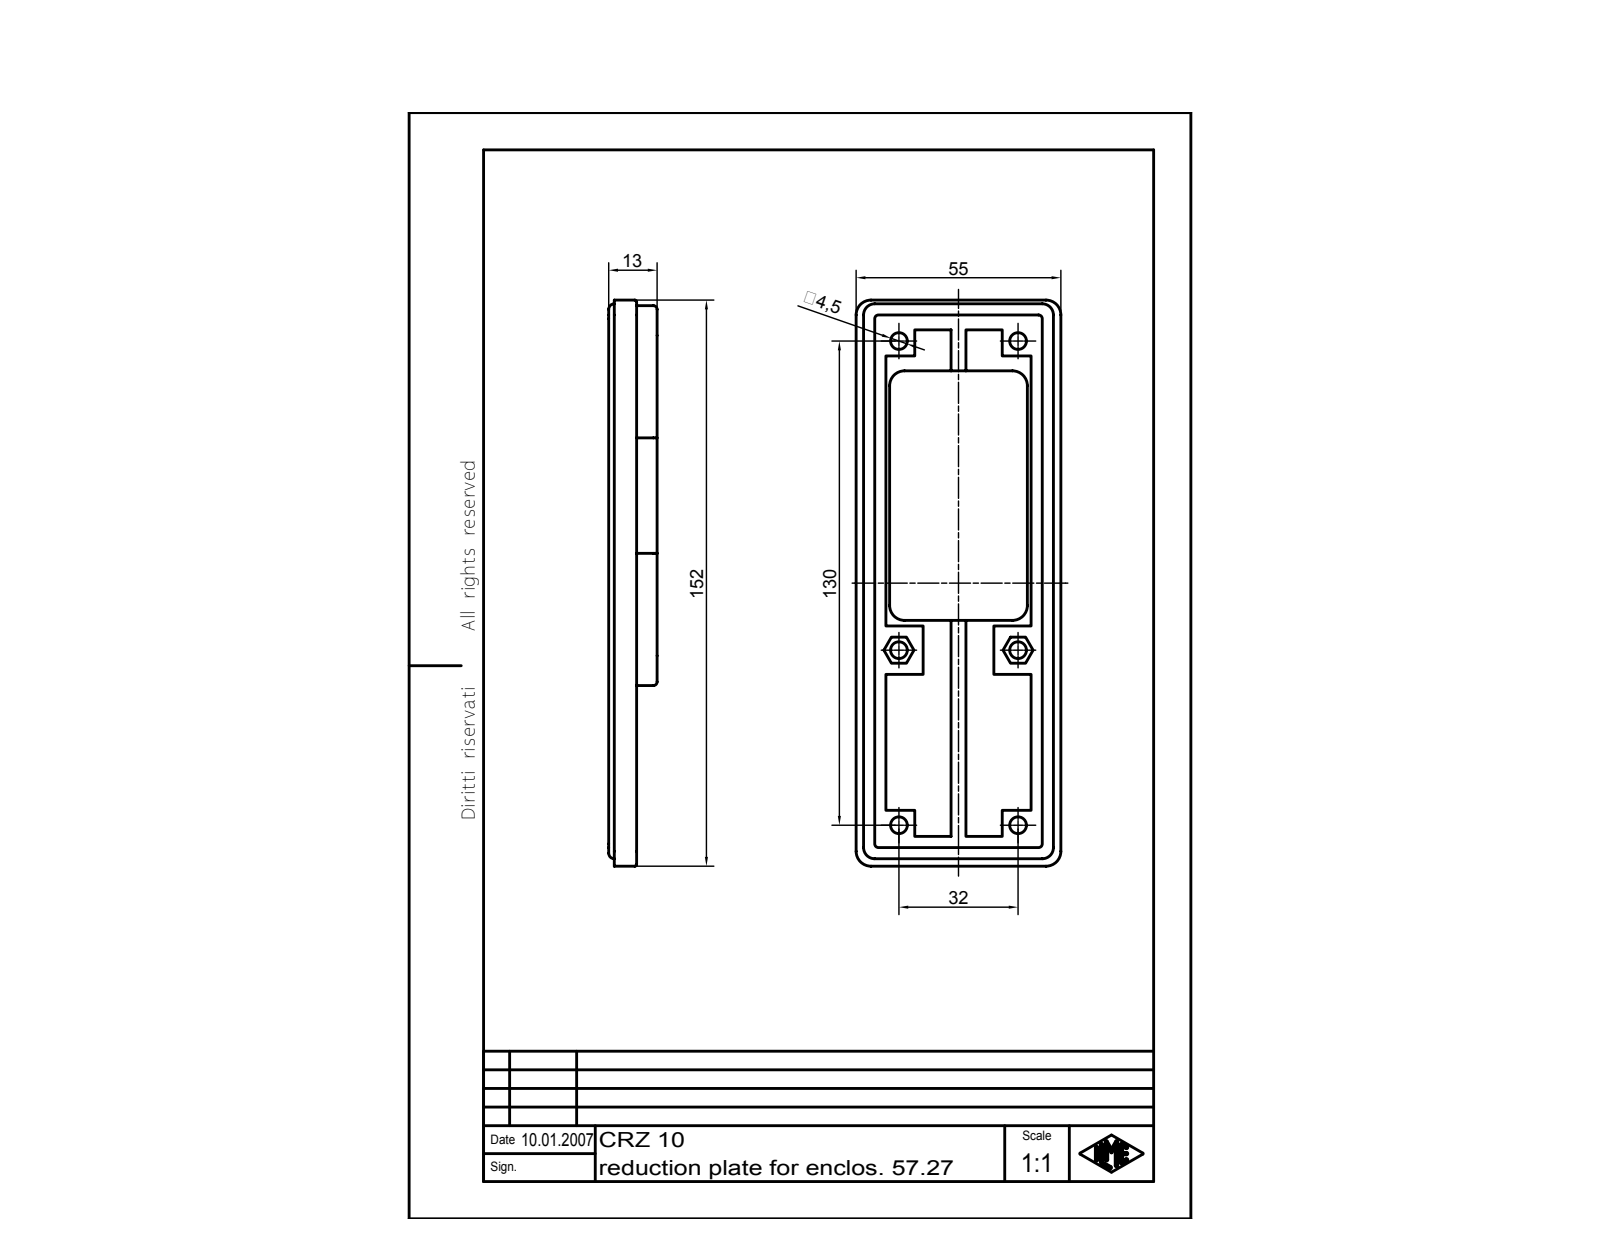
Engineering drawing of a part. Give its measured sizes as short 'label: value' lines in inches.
name: CRZ 10
written by: Autodesk Inventor 7 (AUTOMOTIVE_DESIGN)
unit: in
bodies: 1 solid, 209 faces (107 planar, 82 cylindrical, 20 other)
size: 5.984 × 2.165 × 0.512
volume: 2.057 in³; area: 30.92 in²
holes: 6× ⌀0.177
rounds: 14× R0.004, 8× R0.039, 8× R0.157, 4× R0.02, 4× R0.059, 4× R0.197, 4× R0.315
face distances: 0.118, 0.236, 2.165, 0.315, 1.909, 1.85, 0.069, 0.187, 1.978, 2.096
hole spacings: 1.26, 1.85, 2.239, 3.268, 3.502, 5.118, 5.271
